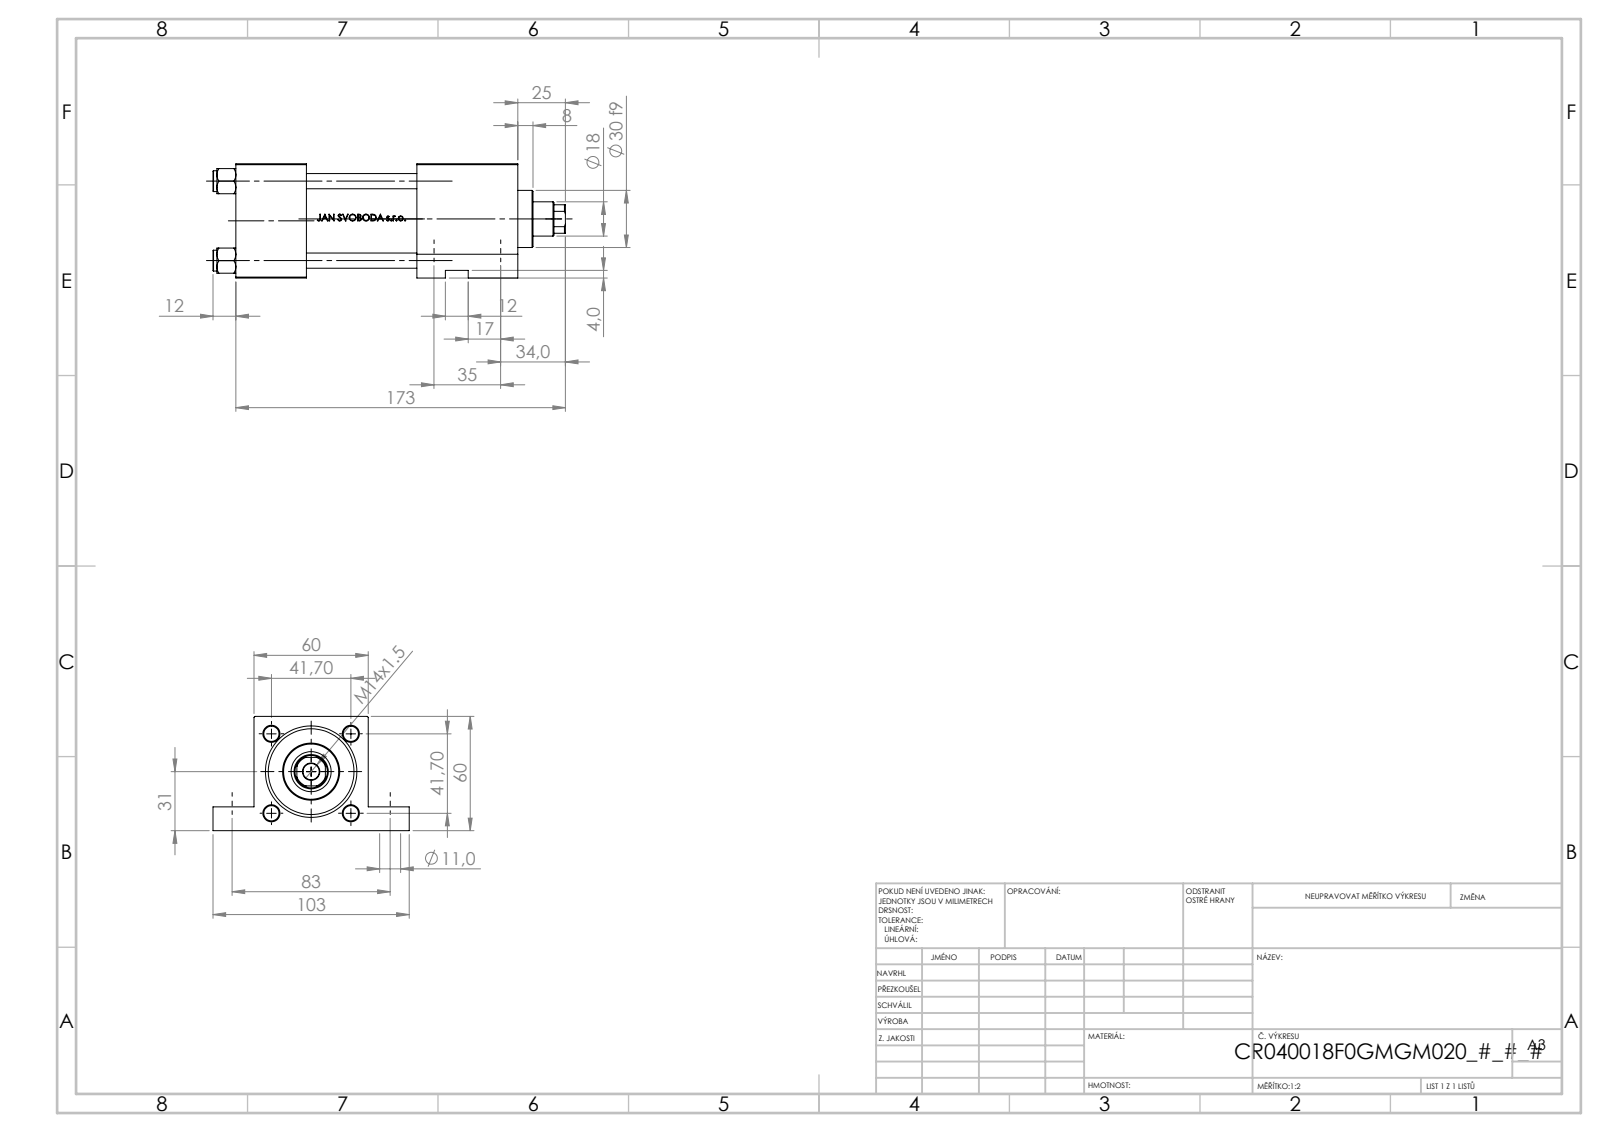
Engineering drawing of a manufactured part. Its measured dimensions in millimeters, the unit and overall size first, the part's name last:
Units: millimetres
Overall size (bounding box): 185 × 103 × 60
Round holes (diameter × count): ⌀8 ×4, ⌀7 ×2, ⌀11 ×2, ⌀11 ×2, ⌀24 ×2, ⌀8.5 ×1, ⌀16 ×1, ⌀16.66 ×1, ⌀18 ×1, ⌀21 ×1, ⌀31 ×1, ⌀40 ×1
Round bosses / shafts (diameter × count): ⌀11 ×4, ⌀46 ×1, ⌀30 ×1
Partial cylindrical surfaces — rounded edges, fillets, slot ends (radius × count): R8.5 ×1
Main face-to-face distances: 60, 37, 148, 111, 95, 58, 53, 119.3, 82.3, 24.3
Hole centre spacings: 41.7, 28.79, 30.2, 35, 58.97, 83, 90.08, 92.5
Volume: 423 048 mm³ · Surface area: 111 805 mm²
Bodies: 11 solids, 1118 faces (437 planar, 141 cylindrical, 540 other)
Part name (STEP PRODUCT): V215_VC_A; NUT_M5_F; V215CR_VCP_F; V215CR_F_Body (+1 more)
STEP written by: SolidWorks 2019 (CONFIG_CONTROL_DESIGN)
